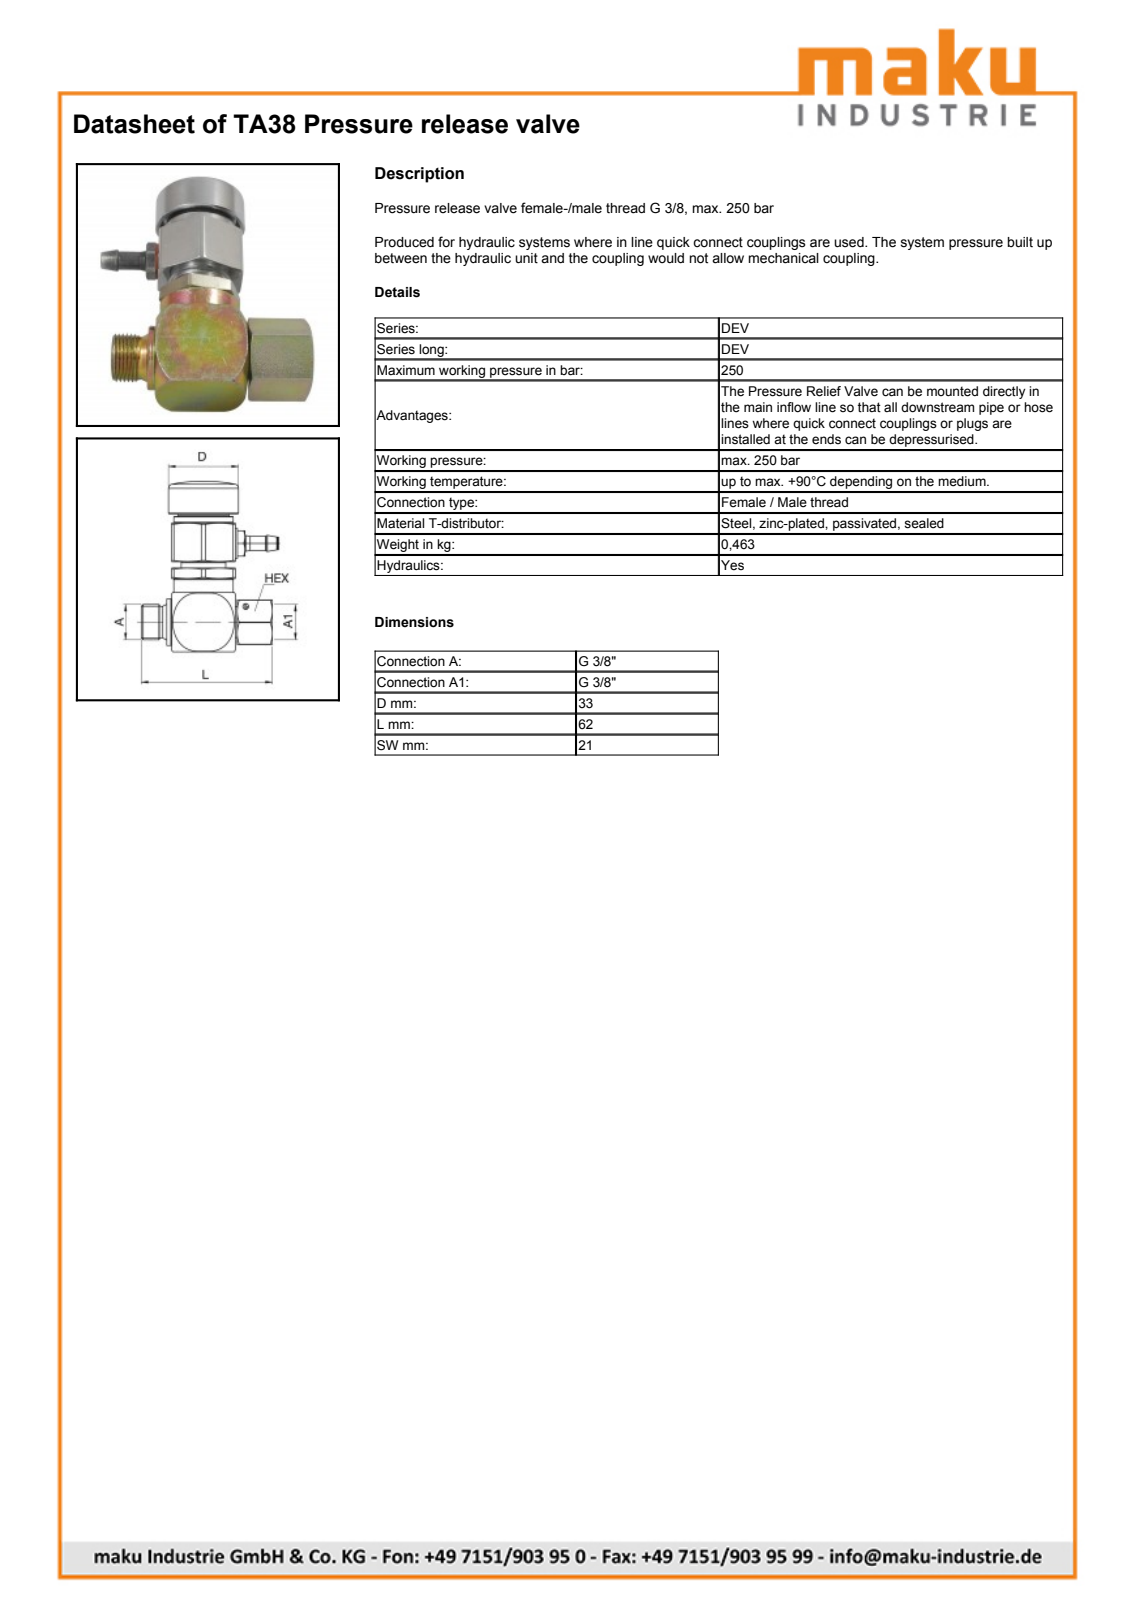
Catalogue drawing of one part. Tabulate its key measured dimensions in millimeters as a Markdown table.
| quantity | value |
| --- | --- |
| part name | TA38 |
| STEP written by | SolidWorks 2009 (AUTOMOTIVE_DESIGN) |
| units | millimeters |
| bodies | 6 solids, 409 faces (94 planar, 140 cylindrical, 175 other) |
| overall size | 80.3 × 64.8 × 33.5 |
| volume | 64 724 mm³ |
| surface area | 25 539 mm² |
| round holes (diameter × count) | 1.5 × 1, 2.7 × 1, 5 × 1, 6 × 1, 7 × 1, 8.6 × 1, 9.4 × 1, 9.59 × 1, 10 × 1, 11.71 × 1, 14.3 × 1, 15 × 1 |
| round bosses / shafts (diameter × count) | 33 × 1, 28.01 × 1, 28 × 1, 24.9 × 1, 24.8 × 1, 24 × 1, 22 × 1, 20.96 × 1 |
| partial cylindrical surfaces (radius × count) | 0.65 × 12, 0.4 × 6, 0.5 × 6, 0.8 × 6, 4.75 × 1, 12.05 × 1, 16.75 × 1, 19.6 × 1 |
| main face-to-face distances | 30, 28, 21, 26.6, 22.7, 3.9, 12.9, 5.3, 39.5, 16.8 |
| hole center spacings | 37.1 |
